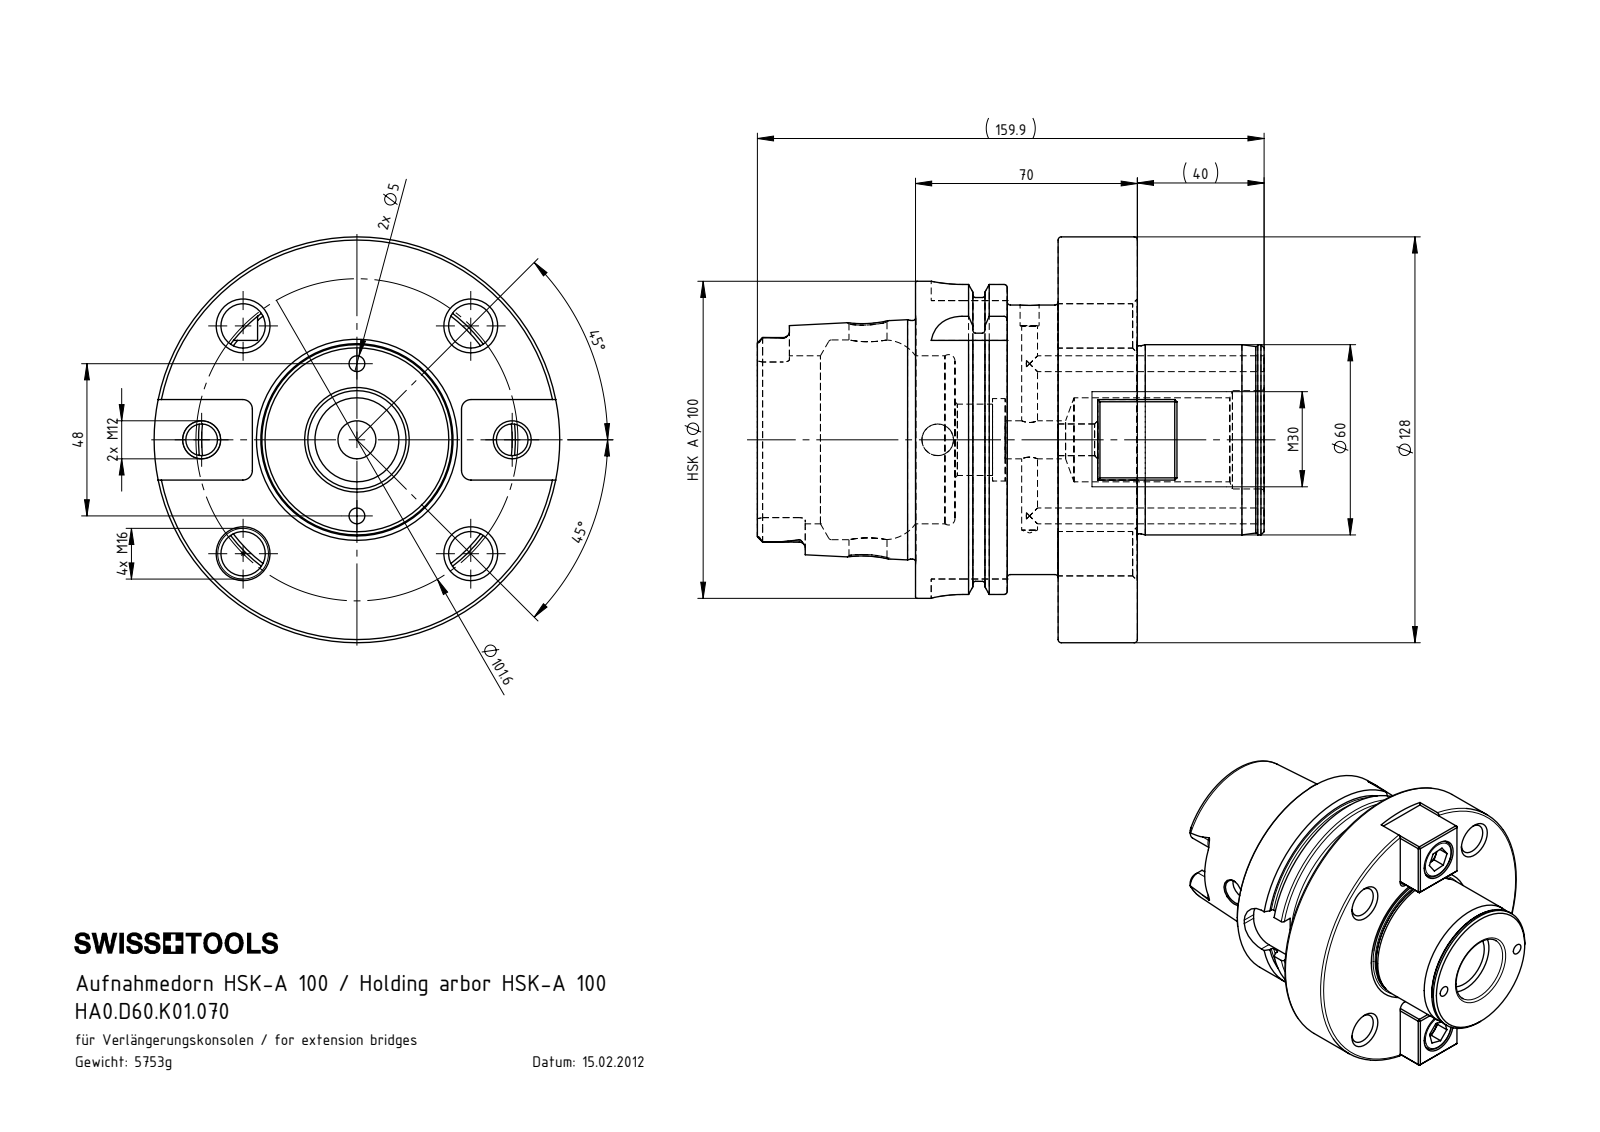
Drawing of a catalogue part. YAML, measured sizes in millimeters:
part_name: "HA0-D60.K01.070_Fertigbearbeitung; ISO 4762 - M12 x 25_PreviewCfg; KVT_MB_600_060; U00-D60.ER1.025 (+1 more)"
step_written_by: "SolidWorks 2022 (AUTOMOTIVE_DESIGN)"
units: millimeters
bodies: {solids: 7, faces: 280, planar: 124, cylindrical: 68, other: 88}
overall_size: [159.9, 128, 128]
volume: 732659
surface_area: 113379
round_holes:
  - {diameter: 14, count: 4}
  - {diameter: 5, count: 3}
  - {diameter: 10, count: 3}
  - {diameter: 12, count: 2}
  - {diameter: 13, count: 2}
  - {diameter: 19, count: 2}
  - {diameter: 22.5, count: 1}
  - {diameter: 26, count: 1}
  - {diameter: 26.5, count: 1}
  - {diameter: 31, count: 1}
  - {diameter: 53, count: 1}
  - {diameter: 63, count: 1}
round_bosses_or_shafts:
  - {diameter: 18, count: 2}
  - {diameter: 12, count: 2}
  - {diameter: 128, count: 1}
  - {diameter: 100, count: 1}
  - {diameter: 91.95, count: 1}
  - {diameter: 85, count: 1}
  - {diameter: 75.26, count: 1}
  - {diameter: 60, count: 1}
partial_cylinders:
  - {radius: 1.9, count: 6}
  - {radius: 3, count: 4}
  - {radius: 4.88, count: 4}
  - {radius: 10, count: 4}
face_to_face_distances: [25, 12.5, 45, 70, 57.5, 110, 25.4, 65, 52.5, 40]
hole_center_spacings: [37.85, 38.23, 50.8, 54.56, 69.86, 71.84, 92.2, 24]
